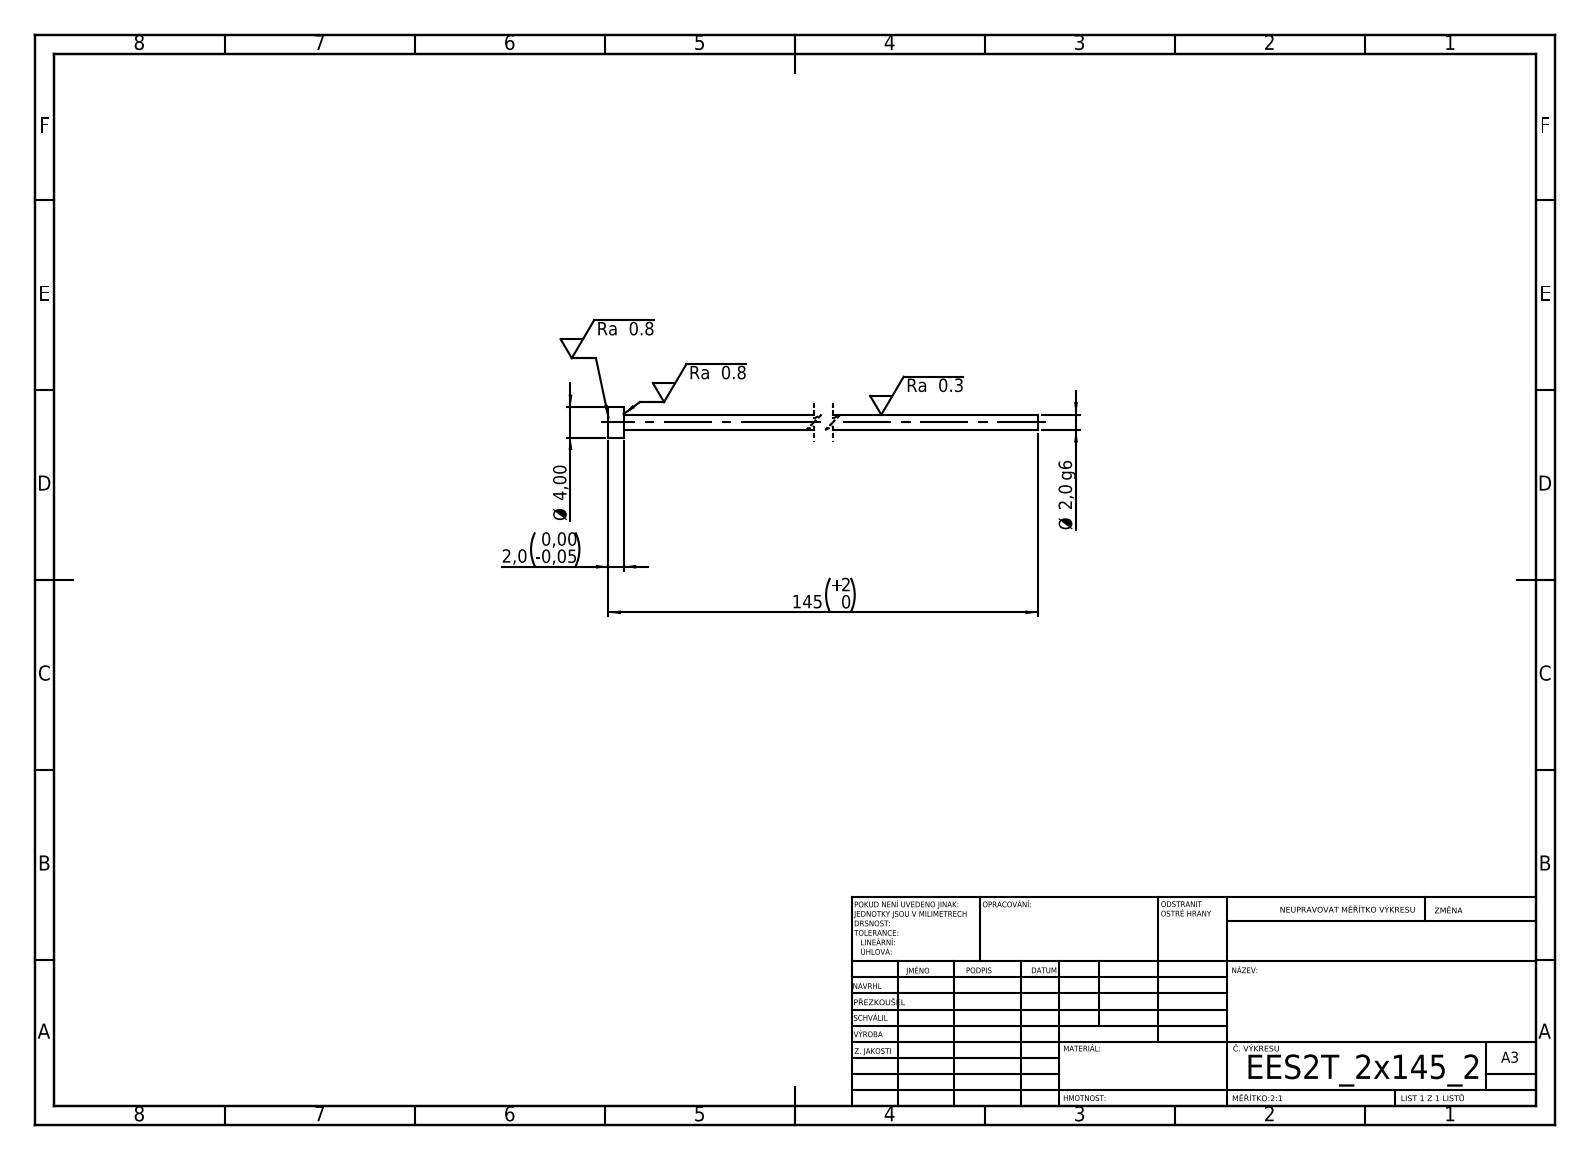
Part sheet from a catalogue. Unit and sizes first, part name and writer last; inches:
Units: inches
Overall size (bounding box): 5.717 × 0.157 × 0.157
Round bosses / shafts (diameter × count): ⌀0.157 ×1, ⌀0.079 ×1
Main face-to-face distances: 0.079, 5.717, 5.638
Volume: 0.029 in³ · Surface area: 1.47 in²
Bodies: 1 solid, 7 faces (3 planar, 4 cylindrical, 0 other)
STEP written by: SolidWorks 2019 (CONFIG_CONTROL_DESIGN)
